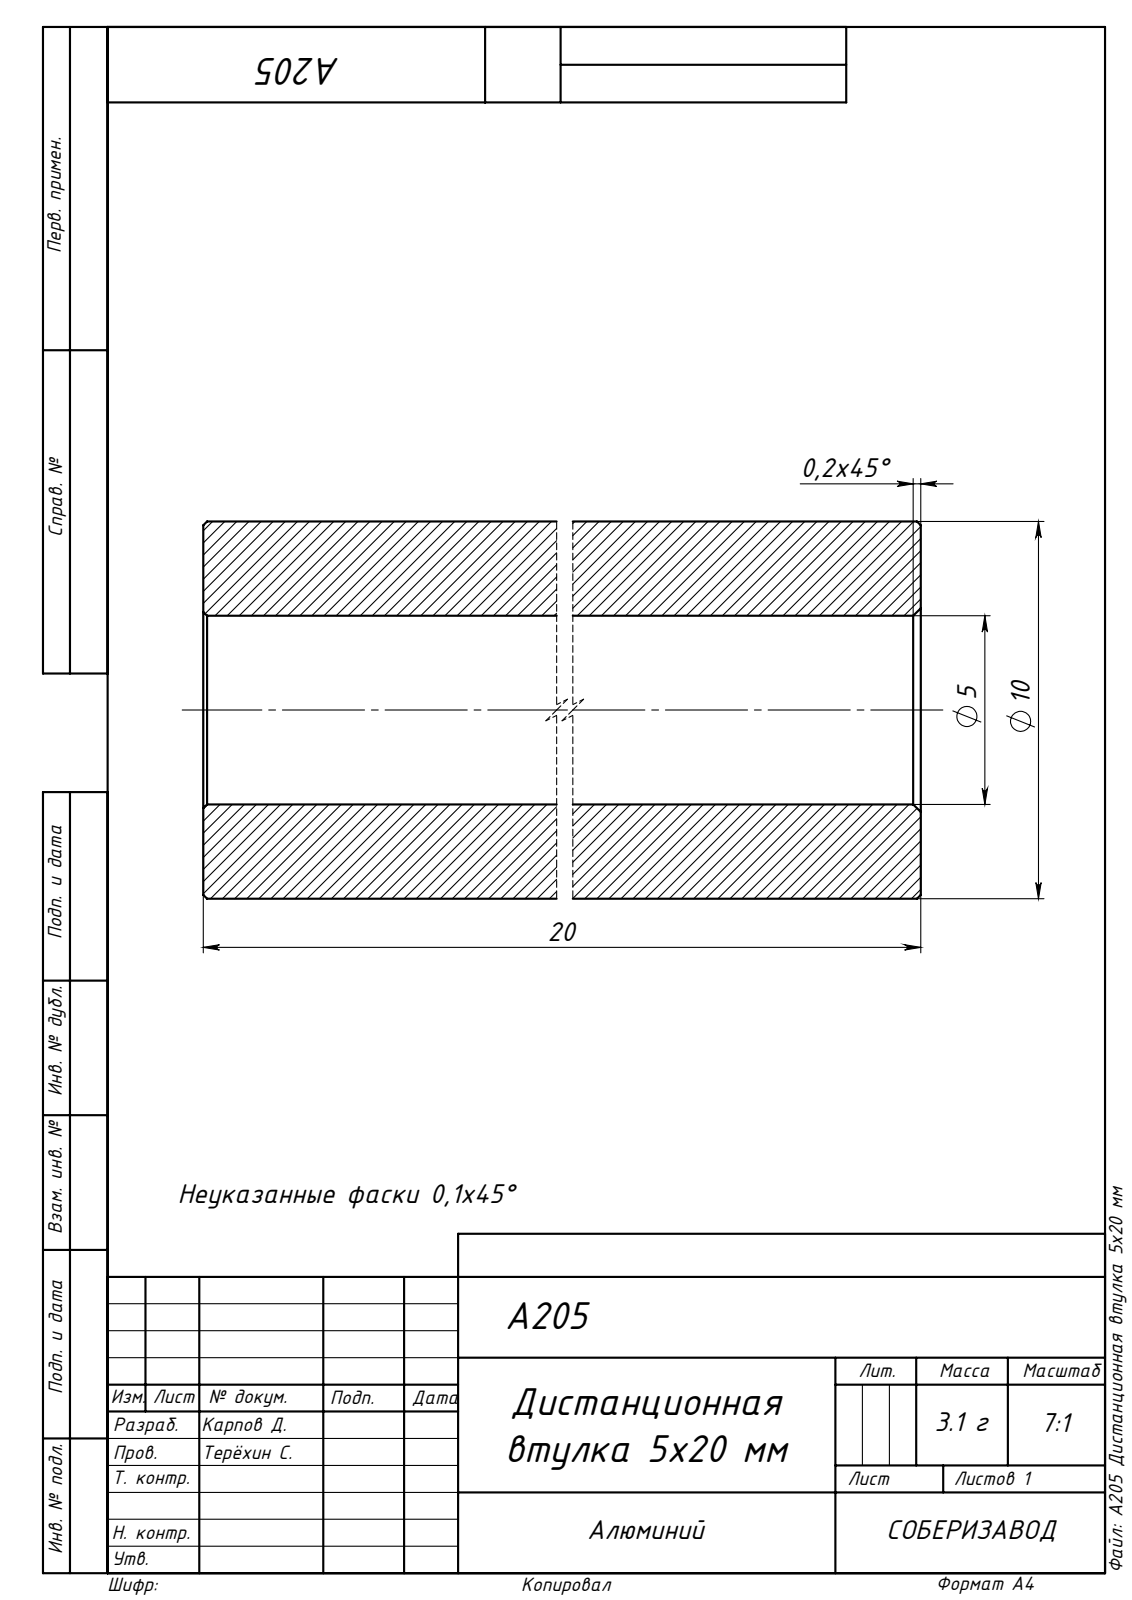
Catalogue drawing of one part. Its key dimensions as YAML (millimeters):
part_name: "A205 Дистанционная втулка 5х20 мм"
step_written_by: "SolidWorks 2020 (AUTOMOTIVE_DESIGN)"
units: millimeters
bodies: {solids: 1, faces: 14, planar: 2, cylindrical: 4, other: 8}
overall_size: [20, 10, 10]
volume: 1177
surface_area: 1054
round_holes:
  - {diameter: 5, count: 1}
round_bosses_or_shafts:
  - {diameter: 10, count: 1}
face_to_face_distances: [20]
